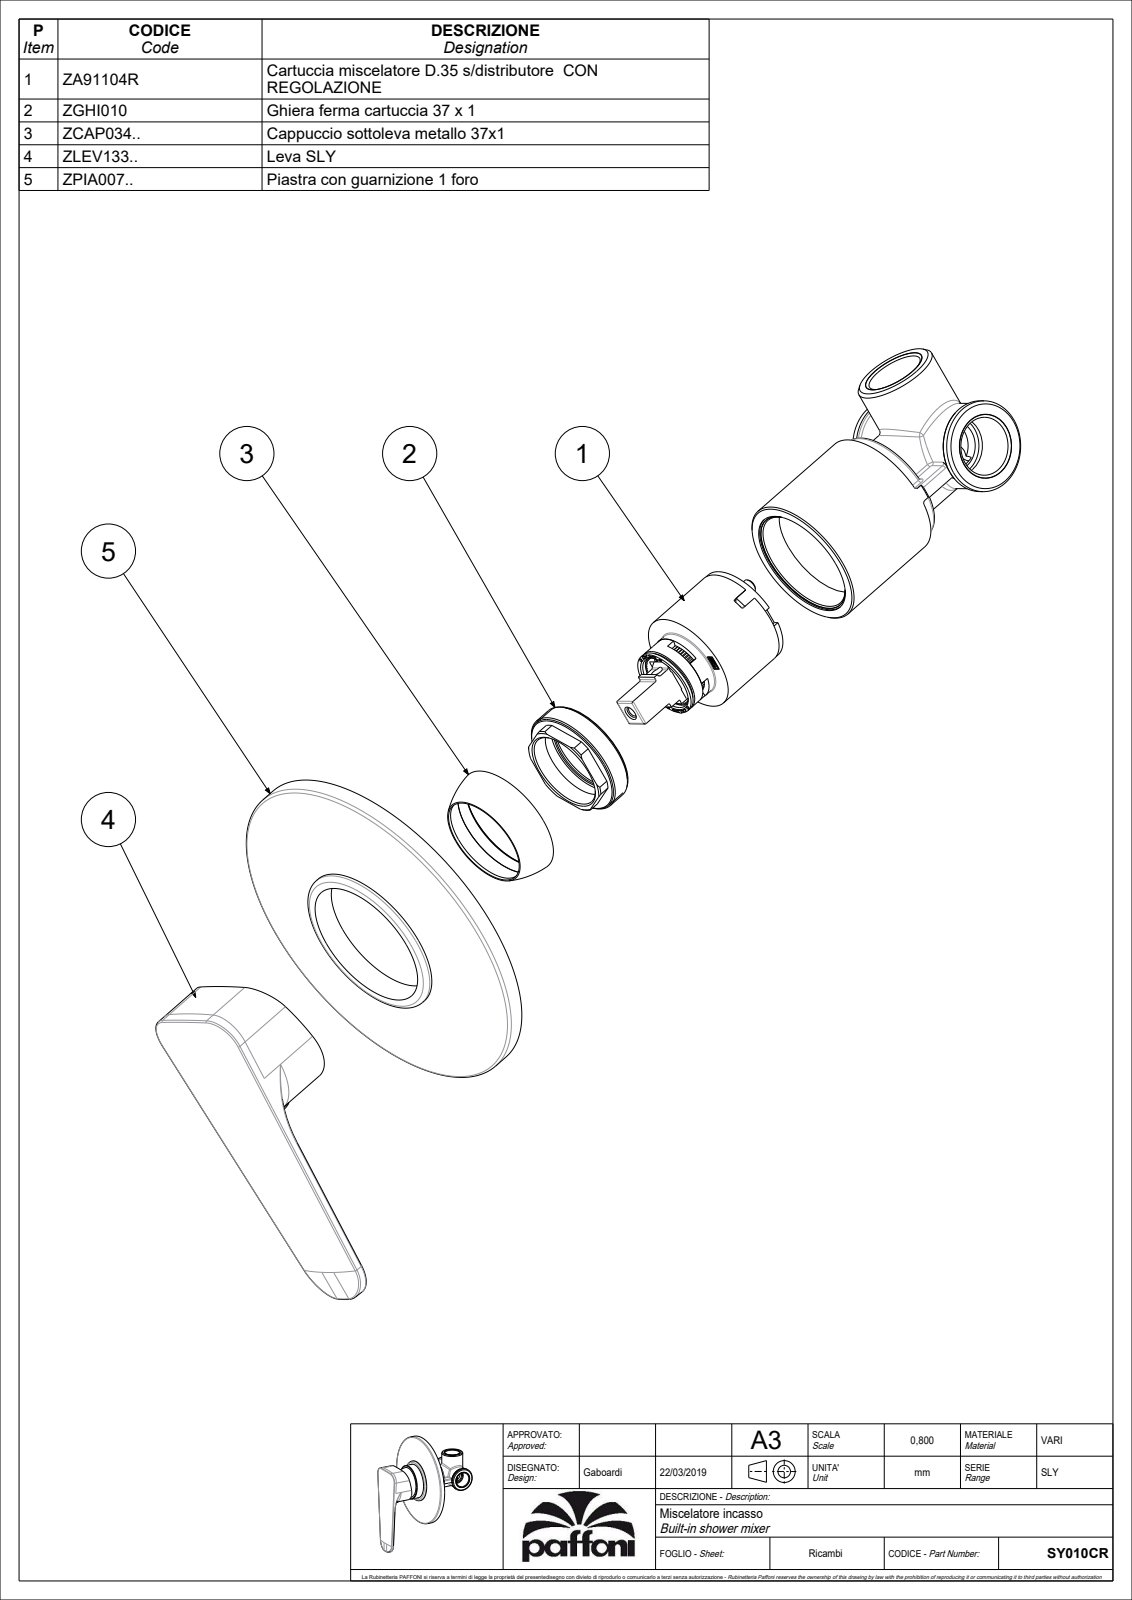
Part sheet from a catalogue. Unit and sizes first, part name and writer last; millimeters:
Units: millimetres
Overall size (bounding box): 148 × 116 × 61.4
Round holes (diameter × count): ⌀3.3 ×2, ⌀4 ×2, ⌀3 ×1, ⌀4.5 ×1, ⌀5 ×1, ⌀19.5 ×1, ⌀19.9 ×1, ⌀26.8 ×1, ⌀29 ×1, ⌀31 ×1, ⌀32.4 ×1, ⌀36 ×1
Round bosses / shafts (diameter × count): ⌀116 ×1, ⌀53 ×1, ⌀44.8 ×1, ⌀35 ×1, ⌀23.5 ×1, ⌀23.4 ×1, ⌀21.8 ×1, ⌀7.6 ×1
Partial cylindrical surfaces — rounded edges, fillets, slot ends (radius × count): R0.5 ×27, R0.15 ×11, R0.3 ×4, R1.5 ×4, R1 ×2, R10 ×2, R4.5 ×1, R7 ×1
Main face-to-face distances: 56.9, 9, 4, 56.6, 1.5, 5.5, 11.5, 9.5, 2.5, 15
Hole centre spacings: 11
Volume: 64 753 mm³ · Surface area: 65 349 mm²
Bodies: 2 solids, 952 faces (564 planar, 217 cylindrical, 171 other)
Part name (STEP PRODUCT): SY010CR
STEP written by: CREO PARAMETRIC BY PTC INC, 2020044 (CONFIG_CONTROL_DESIGN)
